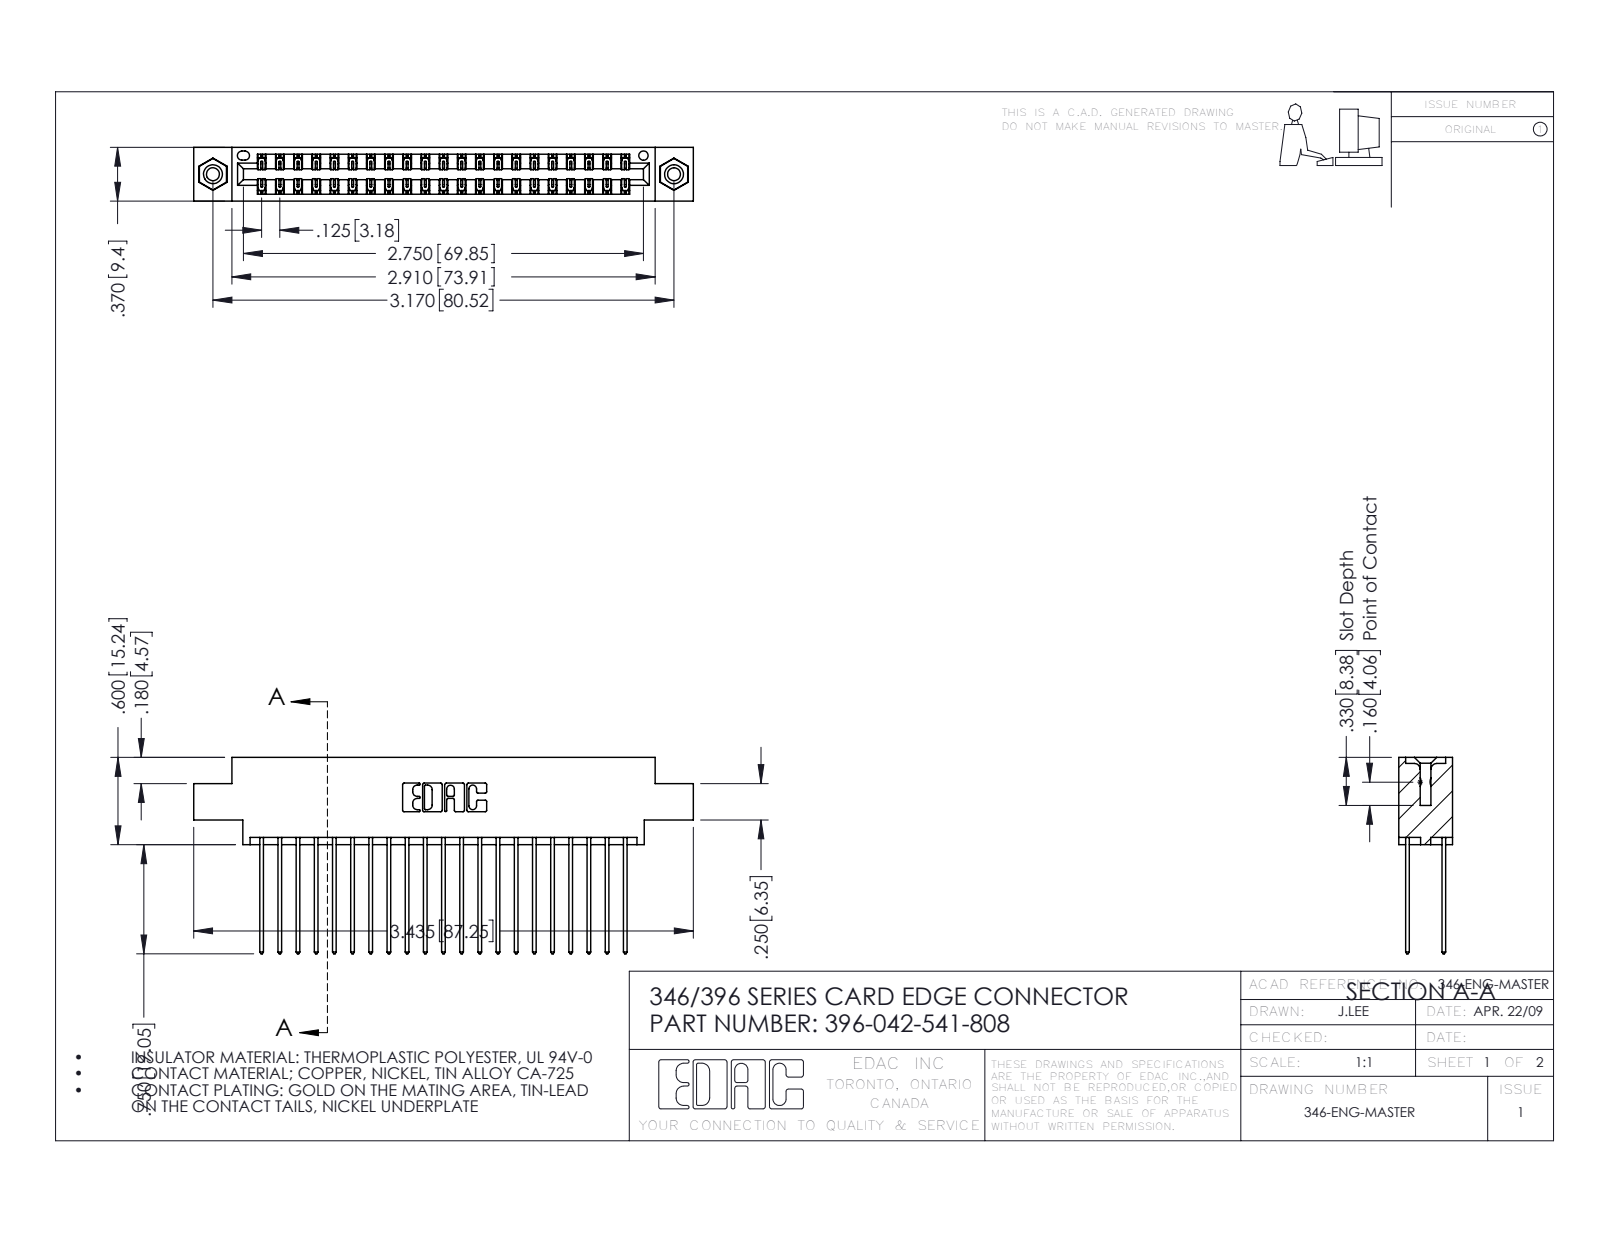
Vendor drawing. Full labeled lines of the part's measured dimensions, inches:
Part name (STEP PRODUCT): 346 Part_0.170 Offset - 0.156 Dia-TI; 396-042-541-808; 345-292-001_345-293-141; 345-250-001_345-250-003-102
STEP written by: SolidWorks 2016 (CONFIG_CONTROL_DESIGN)
Units: inches
Bodies: 45 solids, 2370 faces (1582 planar, 772 cylindrical, 16 other)
Overall size (bounding box): 3.435 × 1.35 × 0.37
Volume: 0.514 in³ · Surface area: 19.54 in²
Round holes (diameter × count): ⌀0.089 ×2, ⌀0.125 ×2, ⌀0.156 ×2, ⌀0.064 ×1
Round bosses / shafts (diameter × count): ⌀0.155 ×2
Partial cylindrical surfaces — rounded edges, fillets, slot ends (radius × count): R0.006 ×63, R0.01 ×42, R0.01 ×22, R0.007 ×6, R0.031 ×6, R0.026 ×3, R0.014 ×2, R0.022 ×2
Main face-to-face distances: 0.048, 0.322, 0.25, 0.072, 0.298, 0.025, 0.37, 0.275, 0.222, 0.225
Hole centre spacings: 0.246, 2.963, 3.17
